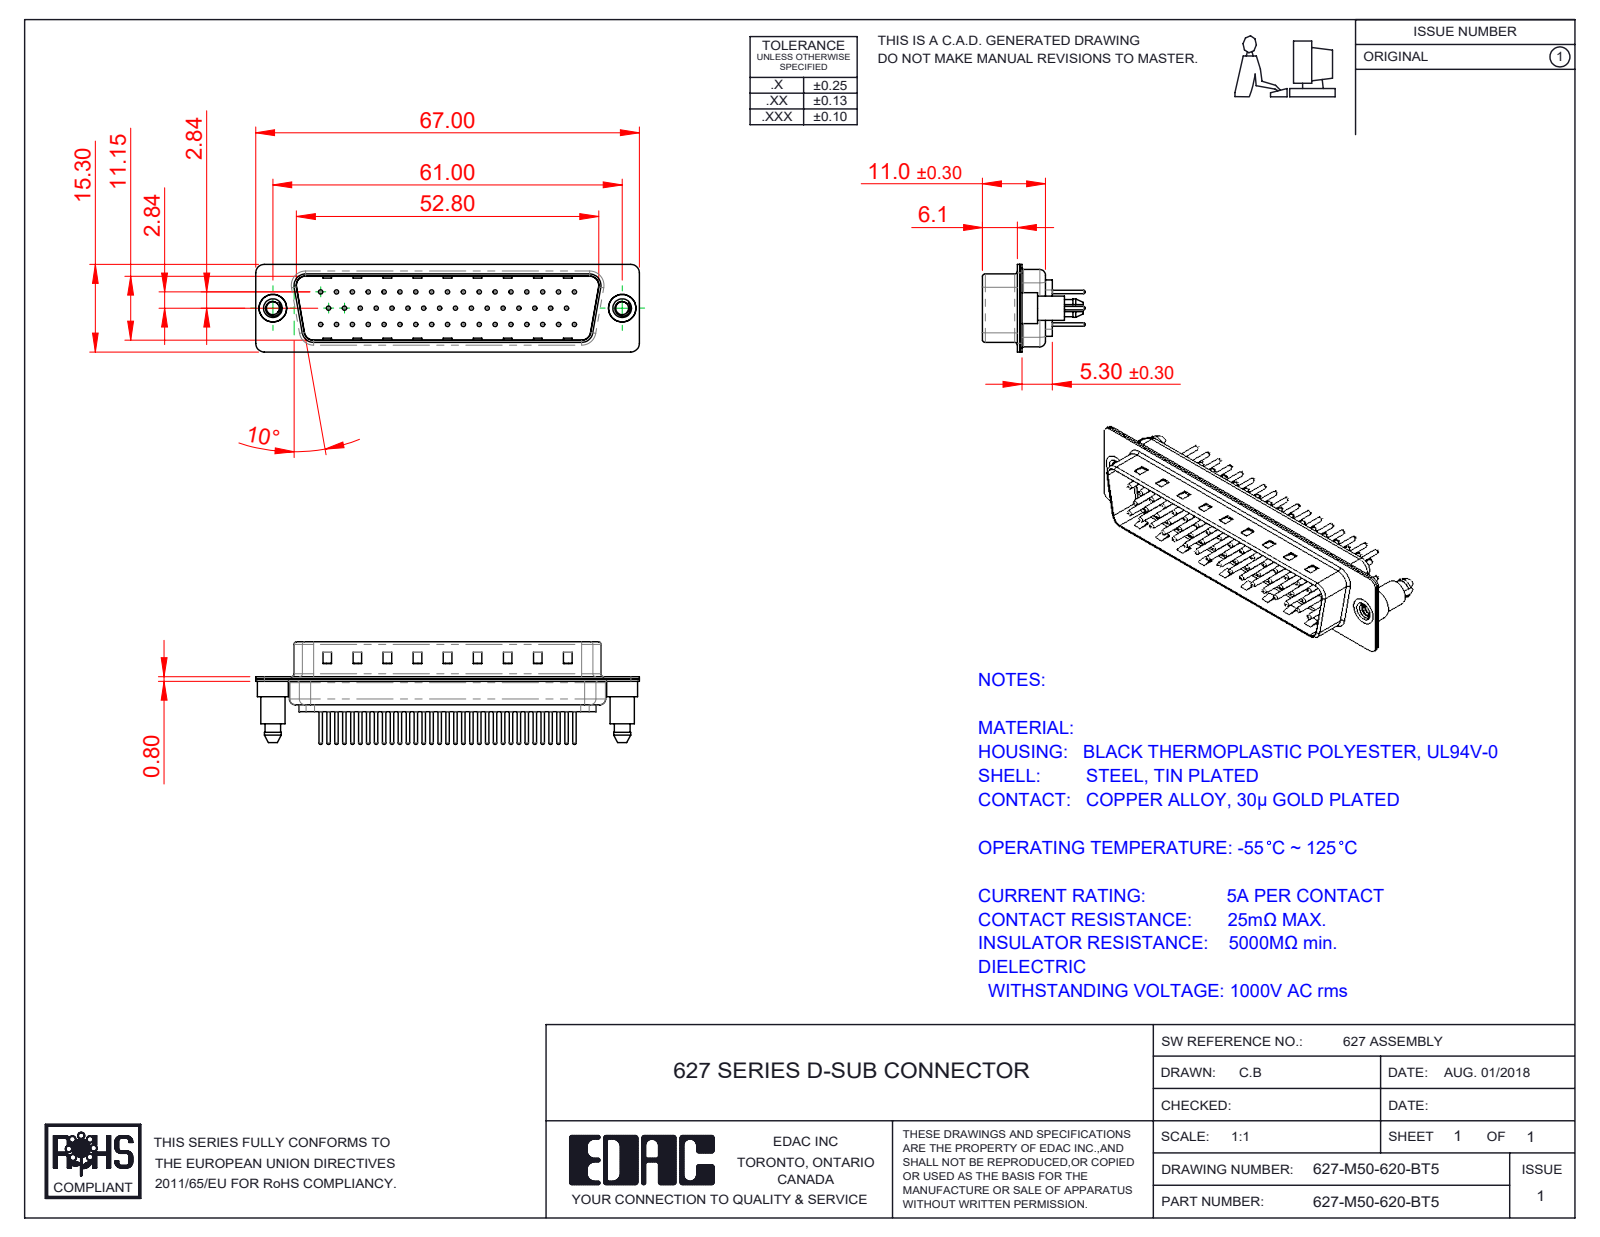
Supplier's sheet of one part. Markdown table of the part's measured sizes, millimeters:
| quantity | value |
| --- | --- |
| part name | 627M Shell Rear_50 Contacts; 627M Contact Row 3_20; 627M Shell Front_50 Contacts; 627-M50-620-BT5 (+4 more) |
| STEP written by | SolidWorks 2020 (CONFIG_CONTROL_DESIGN) |
| units | millimeters |
| bodies | 55 solids, 2312 faces (569 planar, 873 cylindrical, 870 other) |
| overall size | 67 × 17.9 × 15.3 |
| volume | 4 659 mm³ |
| surface area | 11 032 mm² |
| round holes (diameter × count) | 0.75 × 50, 1.6 × 50, 2 × 50, 2.26 × 2, 4 × 2, 4.8 × 2 |
| round bosses / shafts (diameter × count) | 1.5 × 50, 0.6 × 50, 5.4 × 2, 4.9 × 2, 4.25 × 2 |
| partial cylindrical surfaces (radius × count) | 1.5 × 18, 2 × 12, 1.6 × 10, 0.5 × 8, 0.25 × 4, 0.6 × 4, 0.65 × 4, 0.9 × 4 |
| main face-to-face distances | 0.4, 11.55, 5.7, 6.1, 0.78, 0.77, 12.33, 5.3, 12.32, 13.1 |
| hole center spacings | 3.16, 2.77, 5.54, 8.31, 11.08, 13.85, 16.62, 5.03 |
